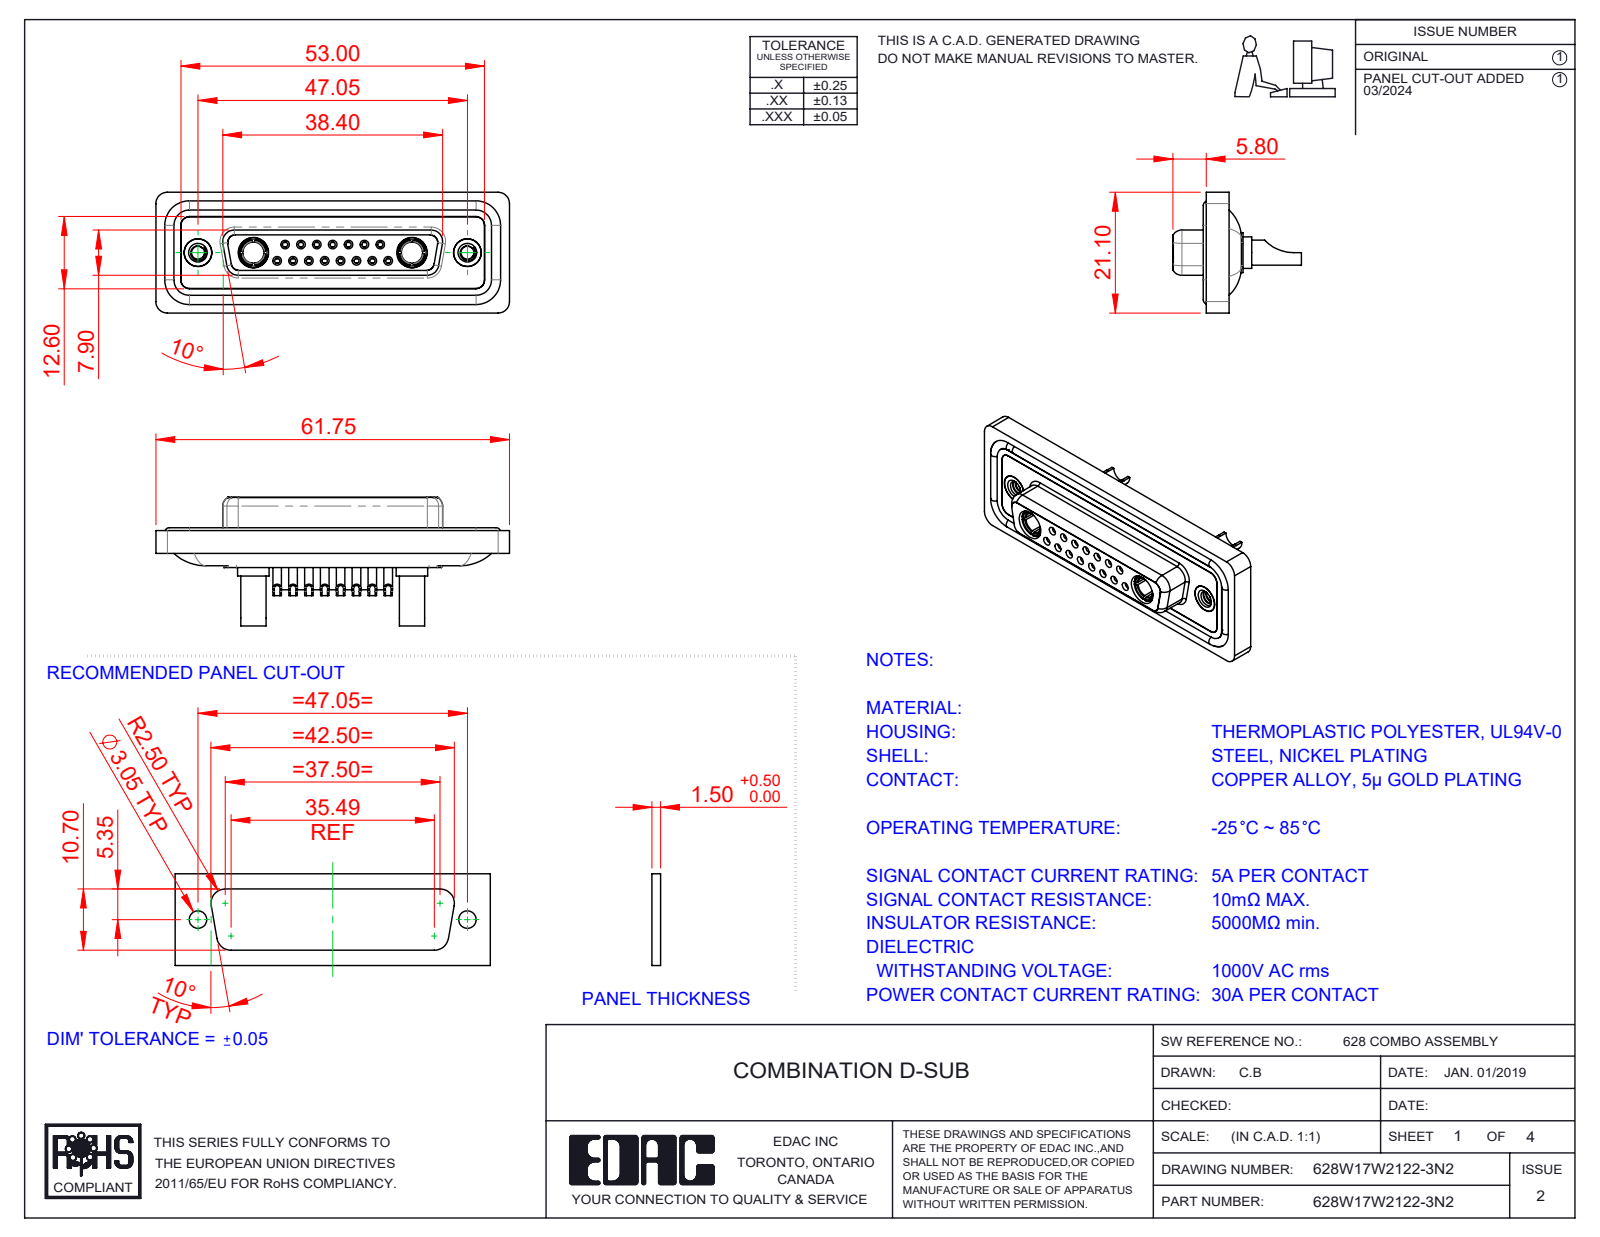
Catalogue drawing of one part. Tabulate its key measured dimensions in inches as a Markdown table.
| quantity | value |
| --- | --- |
| part name | Power Socket_30A SC; 628Combo Waterproof Housing_25 Contacts; 628Combo Threaded Rivet_2; 628Combo Contact Row 1_22 (+5 more) |
| STEP written by | SolidWorks 2023 (CONFIG_CONTROL_DESIGN) |
| units | inches |
| bodies | 26 solids, 1371 faces (424 planar, 555 cylindrical, 392 other) |
| overall size | 2.431 × 0.884 × 0.831 |
| volume | 0.513 in³ |
| surface area | 22.06 in² |
| round holes (diameter × count) | 0.035 × 15, 0.039 × 15, 0.043 × 15, 0.059 × 15, 0.079 × 15, 0.063 × 8, 0.067 × 7, 0.191 × 4, 0.089 × 2, 0.138 × 2, 0.146 × 2, 0.157 × 2 |
| round bosses / shafts (diameter × count) | 0.087 × 15, 0.063 × 11, 0.217 × 2, 0.205 × 2, 0.195 × 2, 0.195 × 2, 0.189 × 2, 0.187 × 2 |
| partial cylindrical surfaces (radius × count) | 0.059 × 22, 0.079 × 18, 0.053 × 8, 0.063 × 8, 0.039 × 6, 0.01 × 4, 0.02 × 4, 0.024 × 4 |
| main face-to-face distances | 0.016, 0.071, 0.293, 0.222, 0.26, 0.02, 0.278, 0.063, 0.114, 0.043 |
| hole center spacings | 0.124, 0.109, 0.327, 0.218, 0.198, 0.198, 0.295, 0.436 |
